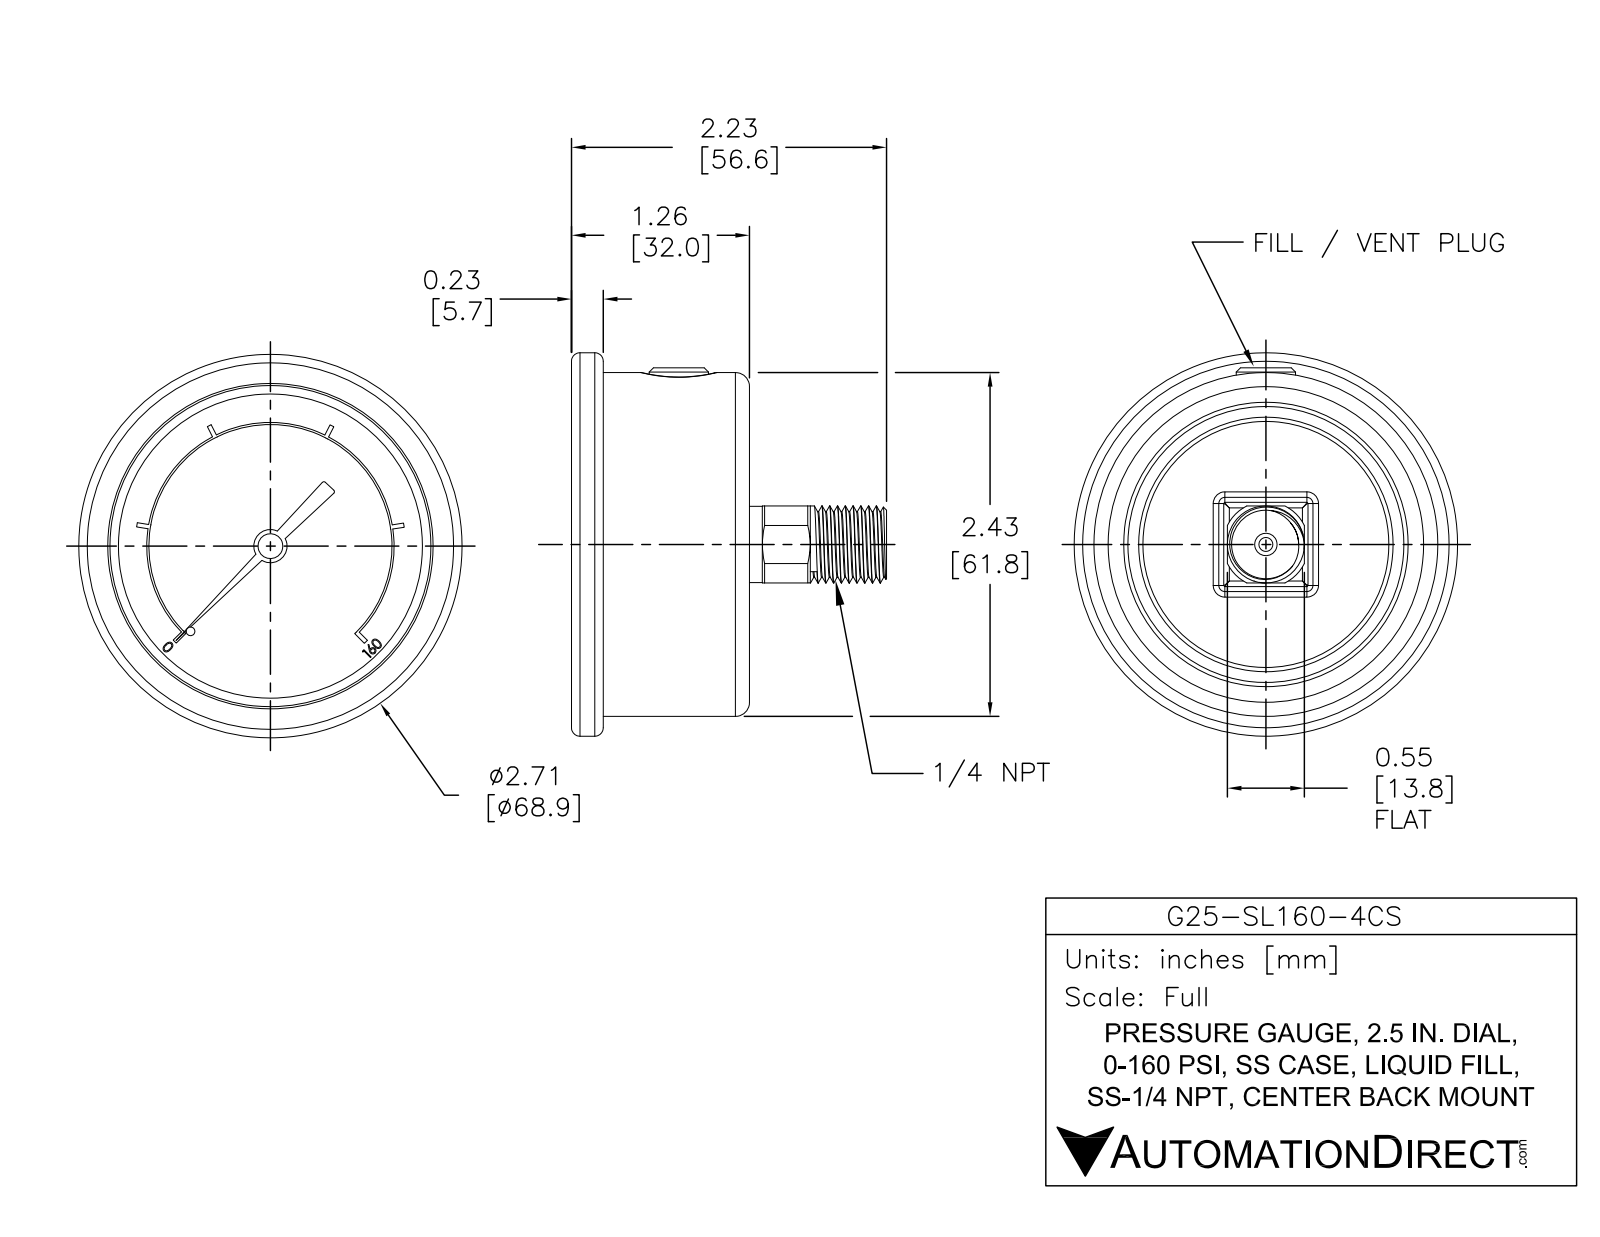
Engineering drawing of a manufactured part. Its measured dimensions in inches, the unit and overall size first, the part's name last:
Units: inches
Overall size (bounding box): 2.713 × 2.713 × 2.23
Round holes (diameter × count): ⌀0.071 ×1, ⌀0.098 ×1, ⌀2.272 ×1
Round bosses / shafts (diameter × count): ⌀2.713 ×1, ⌀2.433 ×1, ⌀0.545 ×1, ⌀0.54 ×1, ⌀0.42 ×1, ⌀0.235 ×1, ⌀0.176 ×1, ⌀0.14 ×1
Partial cylindrical surfaces — rounded edges, fillets, slot ends (radius × count): R0.06 ×8, R0.015 ×2, R0.304 ×1, R0.86 ×1, R0.875 ×1
Main face-to-face distances: 0.95, 1.2, 0.25, 0.06, 1.01, 1.26, 1.035, 0.975, 0.025, 0.225
Volume: 5.168 in³ · Surface area: 24.82 in²
Bodies: 1 solid, 351 faces (211 planar, 83 cylindrical, 57 other)
Part name (STEP PRODUCT): G25-SL160-4CS
STEP written by: SolidWorks 2021 (AUTOMOTIVE_DESIGN)
